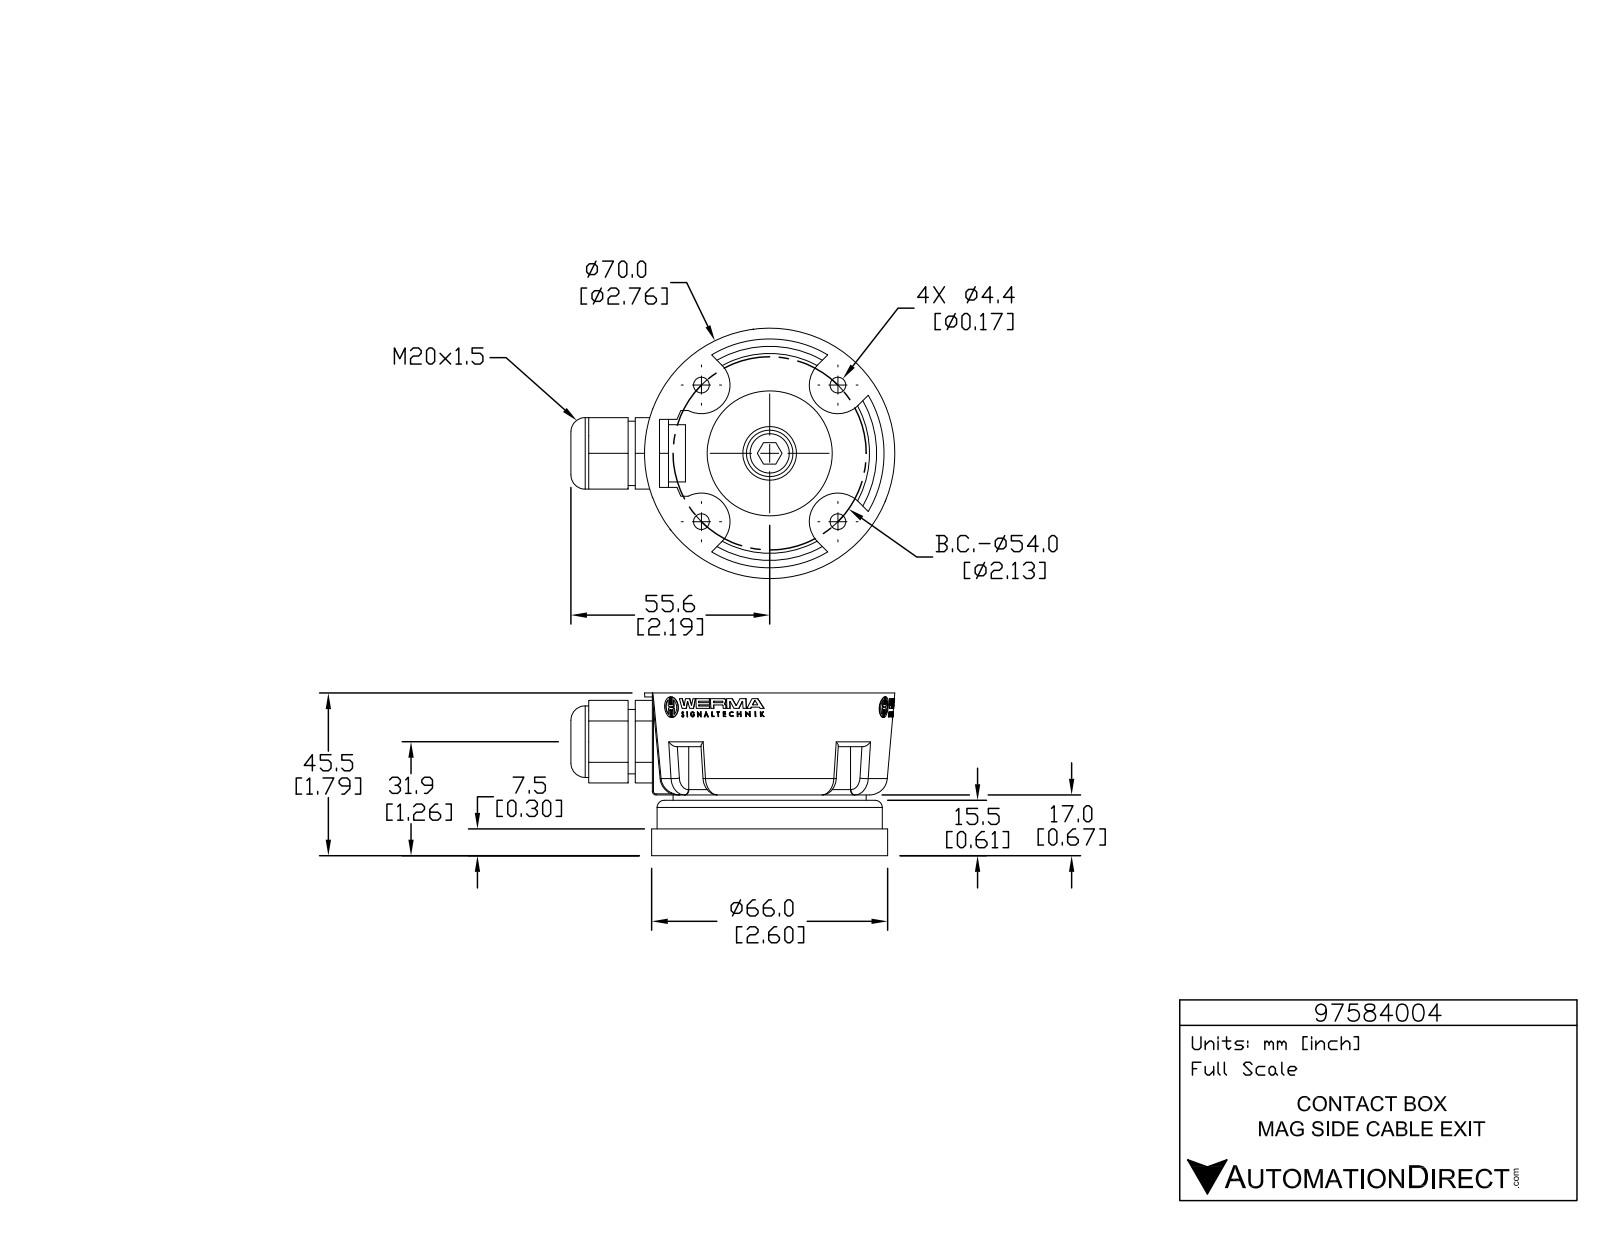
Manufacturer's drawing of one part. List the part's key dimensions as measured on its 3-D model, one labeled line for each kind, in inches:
Part name (STEP PRODUCT): 97584004
STEP written by: SolidWorks 2015 (AUTOMOTIVE_DESIGN)
Units: inches
Bodies: 1 solid, 955 faces (597 planar, 226 cylindrical, 132 other)
Overall size (bounding box): 3.567 × 2.756 × 1.792
Volume: 6.102 in³ · Surface area: 46.86 in²
Round holes (diameter × count): ⌀0.173 ×4, ⌀0.039 ×3, ⌀0.394 ×1
Round bosses / shafts (diameter × count): ⌀0.226 ×3, ⌀0.056 ×3, ⌀2.598 ×1, ⌀2.48 ×1, ⌀2.126 ×1, ⌀1.378 ×1, ⌀0.787 ×1, ⌀0.709 ×1
Partial cylindrical surfaces — rounded edges, fillets, slot ends (radius × count): R0.059 ×8, R0.008 ×6, R0.008 ×6, R0.008 ×6, R0.131 ×6, R0.012 ×4, R0.197 ×4, R0.315 ×4
Main face-to-face distances: 0.118, 0.787, 1.791, 1.004, 0.906, 0.295, 0.886, 0.61, 0.591, 0.177
Hole centre spacings: 1.503, 2.126, 0.365
